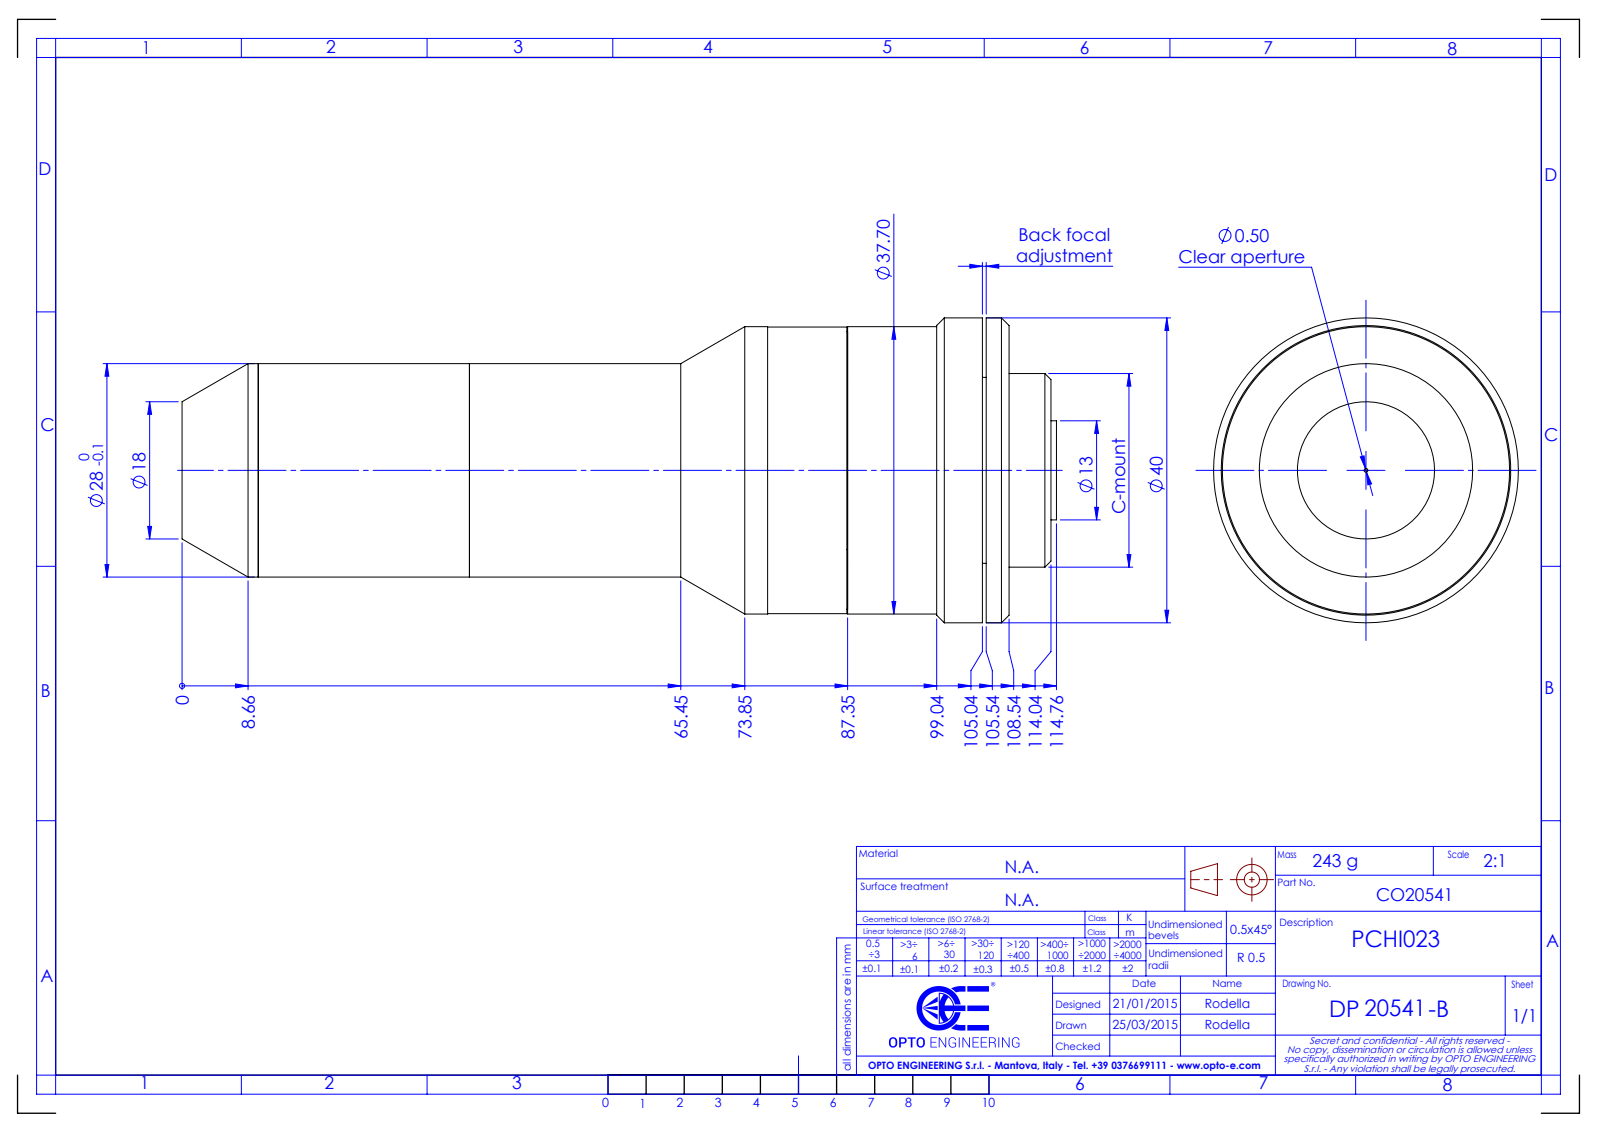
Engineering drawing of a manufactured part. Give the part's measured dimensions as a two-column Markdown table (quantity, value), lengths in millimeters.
| quantity | value |
| --- | --- |
| part name | DP20541-B_PCHI023 |
| STEP written by | SolidWorks 2021 (CONFIG_CONTROL_DESIGN) |
| units | millimeters |
| bodies | 0 solids, 53 faces (15 planar, 28 cylindrical, 10 other) |
| overall size | 114.76 × 40 × 40 |
| round holes (diameter × count) | 0.5 × 1, 5.5 × 1, 22.5 × 1 |
| round bosses / shafts (diameter × count) | 40 × 1, 37.7 × 1, 37.6 × 1, 28 × 1, 25.4 × 1, 22 × 1, 13 × 1 |
| main face-to-face distances | 0.5, 3.5, 3, 17.69, 18.19, 21.19, 77.35, 95.04, 95.54, 98.54 |
